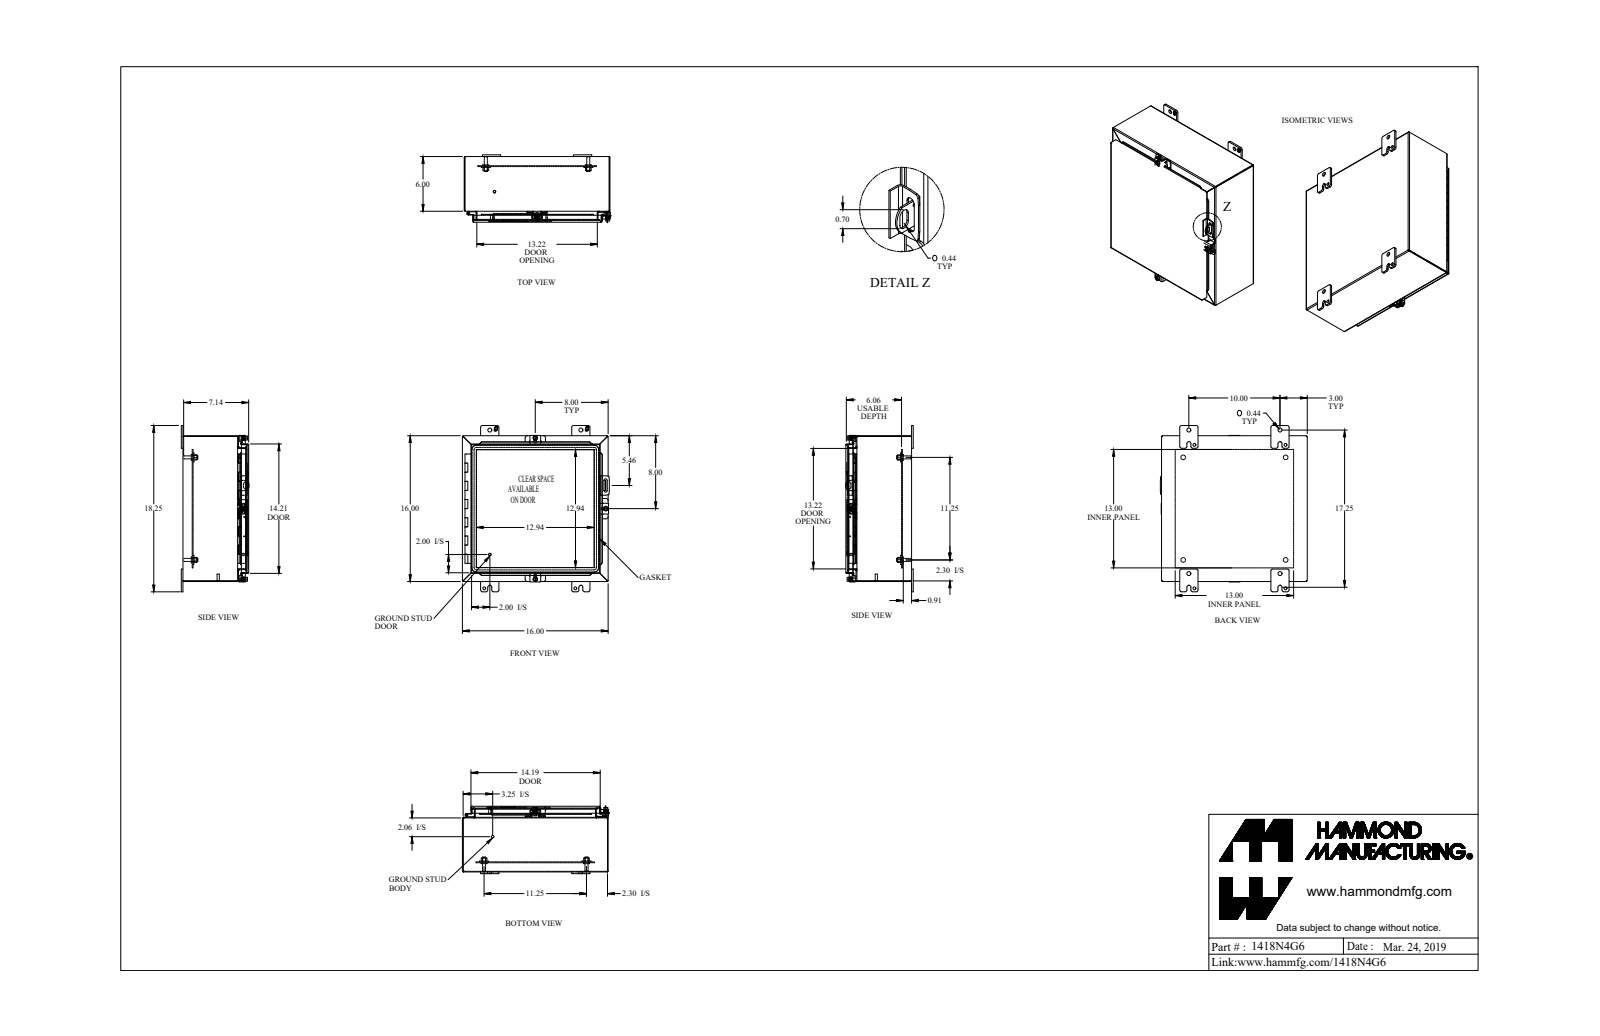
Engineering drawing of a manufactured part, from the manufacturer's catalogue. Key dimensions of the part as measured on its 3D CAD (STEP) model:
Part name (STEP PRODUCT): 1418N4G6_Default
STEP written by: SolidWorks 2019 (CONFIG_CONTROL_DESIGN)
Units: inches
Bodies: 35 solids, 1197 faces (729 planar, 386 cylindrical, 82 other)
Overall size (bounding box): 18.25 × 16.126 × 7.437
Volume: 102.2 in³ · Surface area: 2 682 in²
Round holes (diameter × count): ⌀0.313 ×4, ⌀0.437 ×4, ⌀0.5 ×4, ⌀0.213 ×3, ⌀0.265 ×3, ⌀0.375 ×3, ⌀0.307 ×2, ⌀0.445 ×2, ⌀0.125 ×1, ⌀0.187 ×1
Round bosses / shafts (diameter × count): ⌀0.65 ×4, ⌀0.375 ×4, ⌀0.33 ×4, ⌀0.5 ×3, ⌀0.39 ×3, ⌀0.244 ×3, ⌀1 ×2, ⌀0.281 ×2
Partial cylindrical surfaces — rounded edges, fillets, slot ends (radius × count): R0.188 ×26, R0.036 ×24, R0.108 ×24, R0.25 ×16, R0.048 ×15, R0.143 ×15, R0.045 ×8, R0.125 ×8
Main face-to-face distances: 0.072, 15.928, 0.072, 7.066, 7.138, 7.138, 7.21, 15.856, 16, 0.095
Hole centre spacings: 14.51, 6.013, 11.25, 15.91, 10, 11.25, 14.509, 15.91
